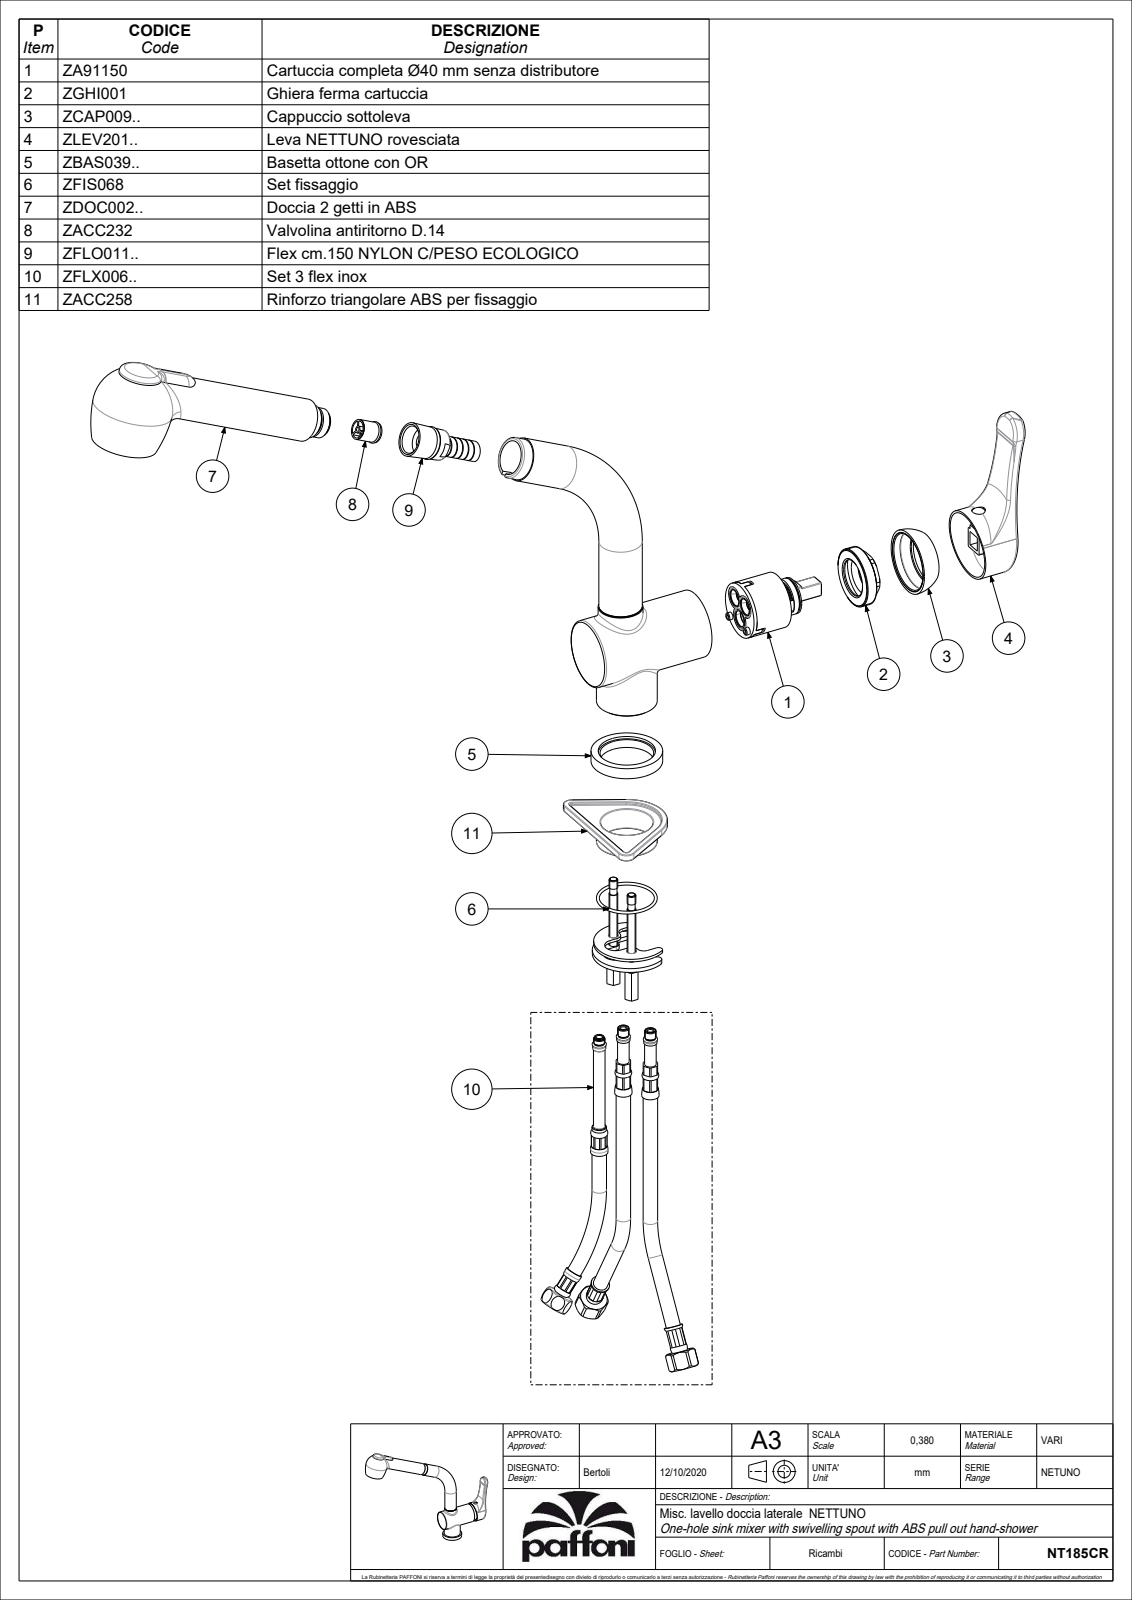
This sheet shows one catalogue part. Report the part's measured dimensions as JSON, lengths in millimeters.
{"part_name": "NT185CR", "step_written_by": "CREO PARAMETRIC BY PTC INC, 2020044 (CONFIG_CONTROL_DESIGN)", "units": "millimeters", "bodies": {"solids": 0, "faces": 177, "planar": 46, "cylindrical": 48, "other": 83}, "overall_size": [361.1, 308.85, 56], "round_holes": [[16, 1]], "round_bosses_or_shafts": [[30, 2], [50, 1], [49.5, 1], [48, 1], [42, 1], [31, 1], [29.8, 1], [29.5, 1]], "partial_cylinders_radius": [[2, 2], [8, 2], [135, 2], [1, 1], [4.7, 1], [10, 1], [11.5, 1], [13, 1]], "face_to_face_distances": [8, 7.95, 84.3, 76.3, 8.5, 3.5, 5, 3, 58.99, 55.99]}
